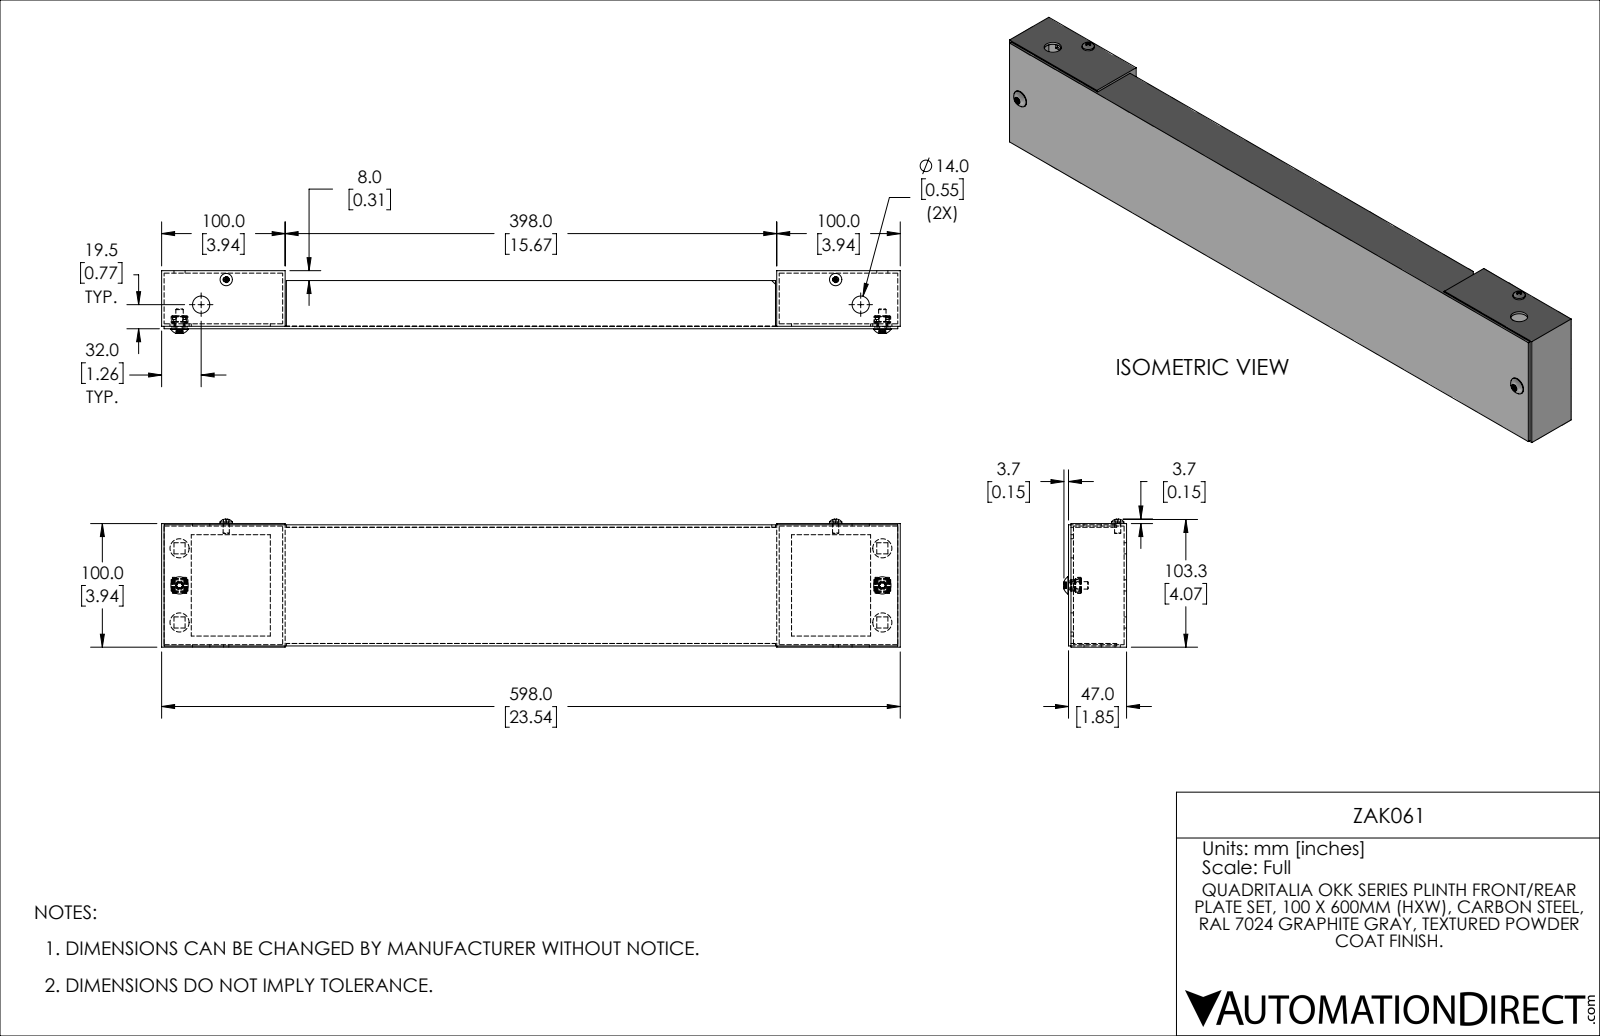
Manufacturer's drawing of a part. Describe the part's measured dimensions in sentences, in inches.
The part is named "ZAK061". Its 3-D file was written by "SolidWorks 2021 (CONFIG_CONTROL_DESIGN)". It is 11 solids with 393 faces: 243 planar, 132 cylindrical and 18 other. Overall it measures 23.543 by 4.084 by 1.996 inches. Its volume is 18.16 cubic inches and its surface area 471.9 square inches. Round holes: 4 of diameter 0.61, 2 of diameter 0.167, 2 of diameter 0.194, 2 of diameter 0.276, 2 of diameter 0.551. Round bosses or shafts: 2 of diameter 0.551, 2 of diameter 0.394, 2 of diameter 0.236, 2 of diameter 0.197. Partial cylindrical surfaces (rounded edges, fillets, slot ends): 42 of radius 0.02, 28 of radius 0.01, 18 of radius 0.039. The main face-to-face distances are 0.079, 0.039, 3.858, 3.78, 1.772, 3.819, 1.693, 1.85, 0.118, 3.898. The hole center spacings are 1.181, 22.433, 22.402, 1.13, 2.362, 20.24, 22.526, 19.425.
